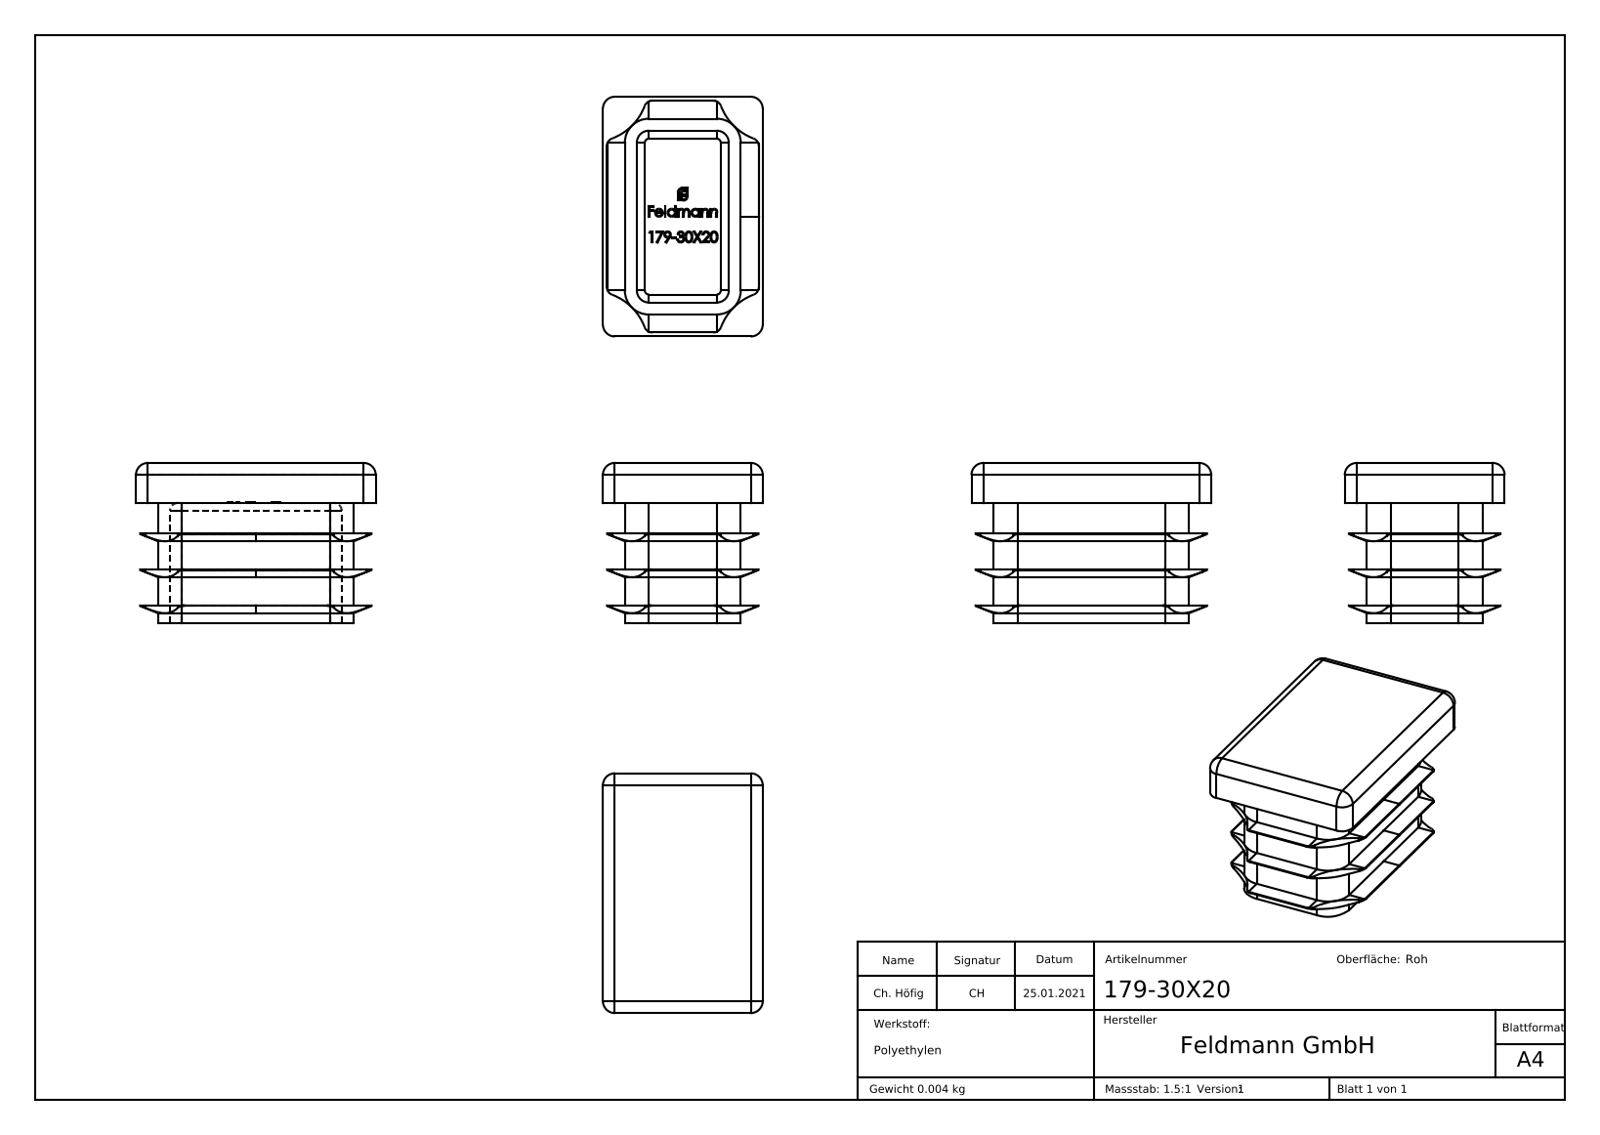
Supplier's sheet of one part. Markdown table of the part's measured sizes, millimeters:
| quantity | value |
| --- | --- |
| part name | 179-30X20 |
| STEP written by | SolidWorks 2018 (CONFIG_CONTROL_DESIGN) |
| units | millimeters |
| bodies | 1 solid, 450 faces (220 planar, 83 cylindrical, 147 other) |
| overall size | 30 × 20 × 20 |
| volume | 4 719 mm³ |
| surface area | 4 346 mm² |
| partial cylindrical surfaces (radius × count) | 1 × 12, 1.5 × 12, 3 × 4, 7 × 4 |
| main face-to-face distances | 1.5, 13, 5, 2.75, 4.25, 4.5, 11.5, 14.5, 23, 20 |
